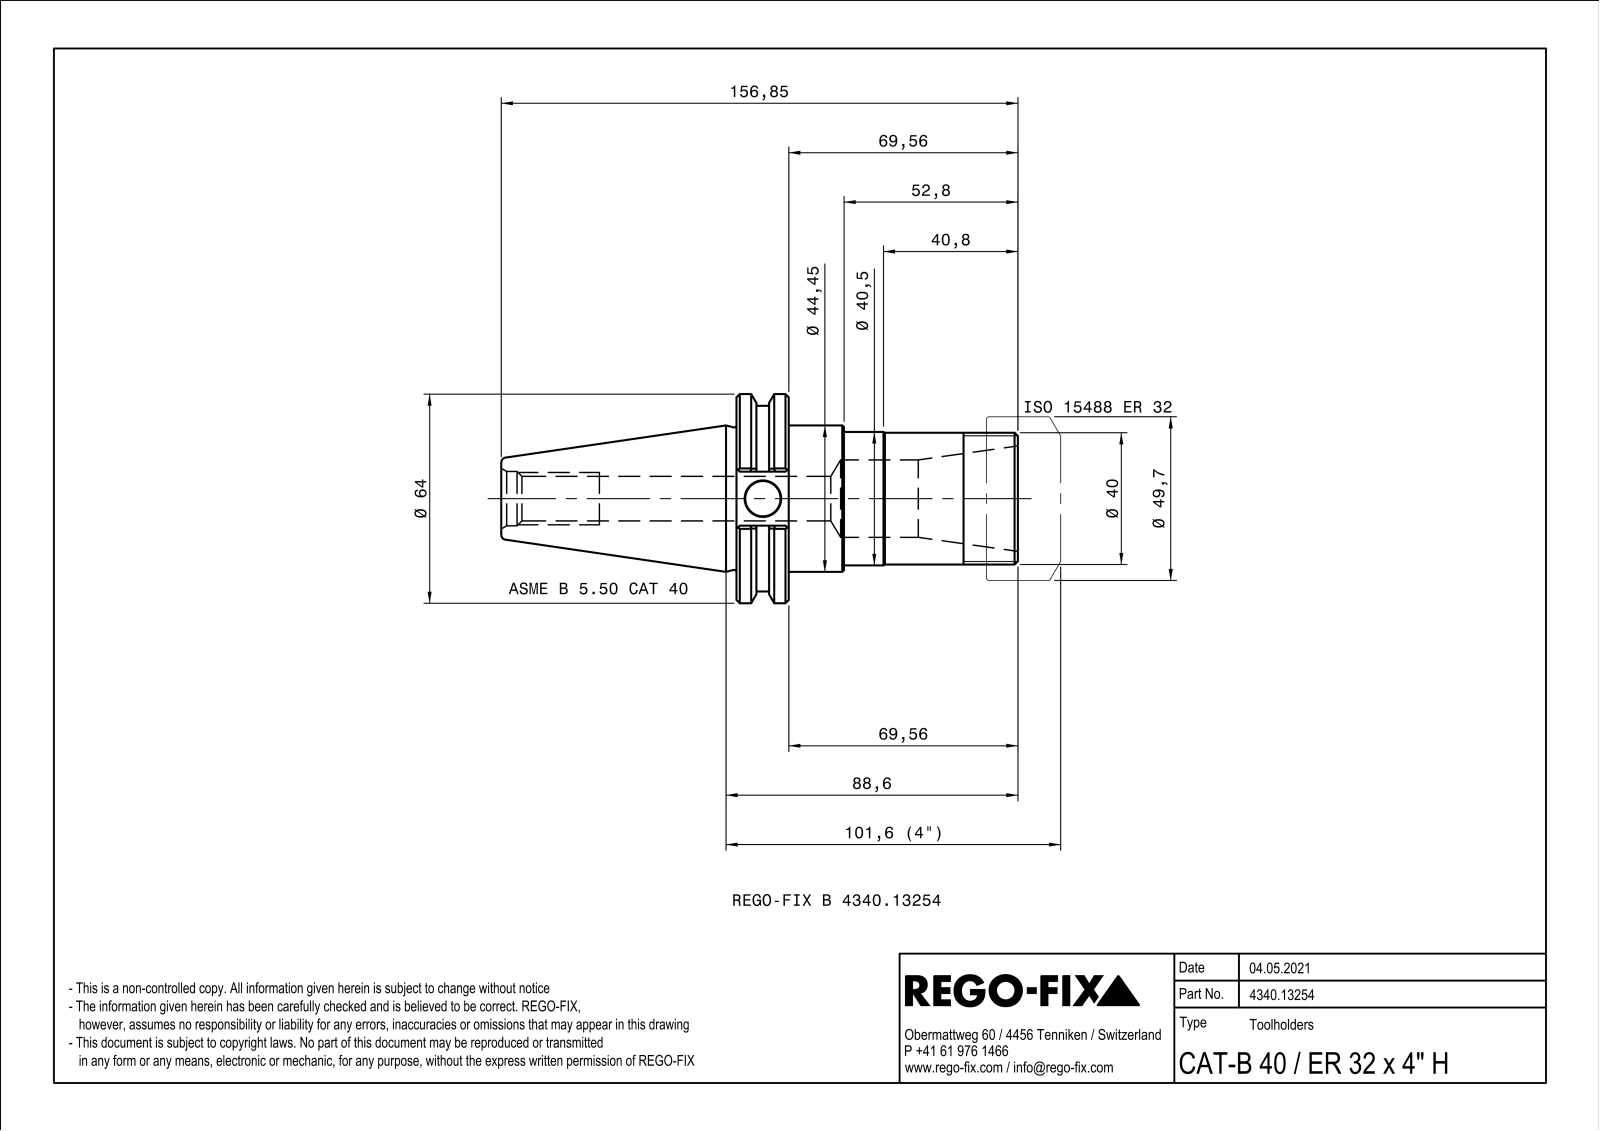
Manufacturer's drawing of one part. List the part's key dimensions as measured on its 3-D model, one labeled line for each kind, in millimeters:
Part name (STEP PRODUCT): NOCUT
STEP written by: SIEMENS PLM Software Solid Edge ST10 (AUTOMOTIVE_DESIGN)
Units: millimetres
Bodies: 1 solid, 114 faces (32 planar, 33 cylindrical, 49 other)
Overall size (bounding box): 156.85 × 63.5 × 60.79
Volume: 160 240 mm³ · Surface area: 34 373 mm²
Round holes (diameter × count): ⌀3.24 ×2, ⌀3.9 ×2, ⌀10.7 ×1, ⌀13.53 ×1, ⌀16.5 ×1, ⌀23.5 ×1
Round bosses / shafts (diameter × count): ⌀63.5 ×1, ⌀56.36 ×1, ⌀44.45 ×1, ⌀40.5 ×1, ⌀40 ×1
Partial cylindrical surfaces — rounded edges, fillets, slot ends (radius × count): R0.5 ×4
Main face-to-face distances: 15.87, 69.56, 85.43, 47.33, 16.38, 156.85, 87.29, 71.42, 75.55, 5.99
